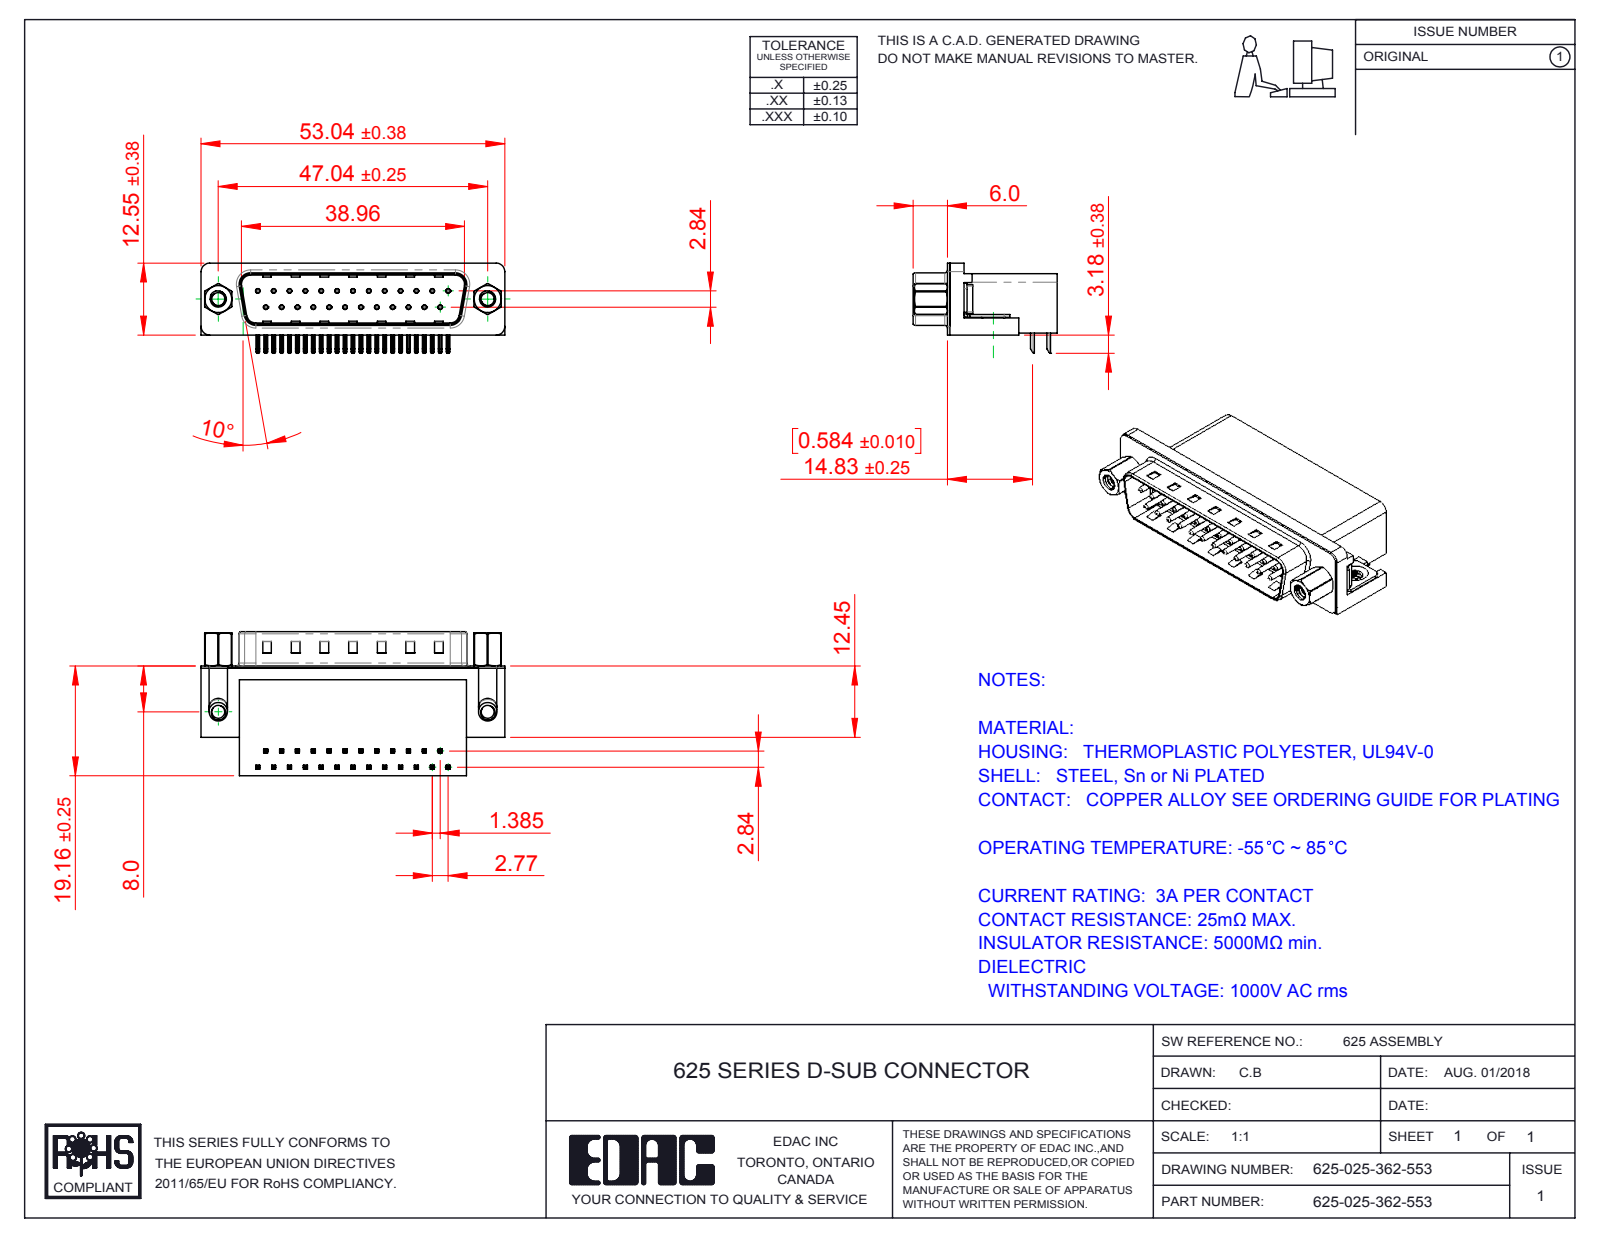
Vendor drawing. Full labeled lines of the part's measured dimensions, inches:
Part name (STEP PRODUCT): 625 Housing_25 Socket; 625 Shell_25 Socket; 625 4-40 Threaded Rivet; 625 Contact Bottom (+4 more)
STEP written by: SolidWorks 2016 (CONFIG_CONTROL_DESIGN)
Units: inches
Bodies: 33 solids, 2423 faces (1429 planar, 745 cylindrical, 249 other)
Overall size (bounding box): 2.088 × 0.991 × 0.619
Volume: 0.573 in³ · Surface area: 14.61 in²
Round holes (diameter × count): ⌀0.014 ×25, ⌀0.031 ×25, ⌀0.089 ×4, ⌀0.09 ×2, ⌀0.157 ×2, ⌀0.189 ×2, ⌀0.197 ×2
Round bosses / shafts (diameter × count): ⌀0.03 ×25, ⌀0.193 ×2, ⌀0.187 ×2, ⌀0.154 ×2, ⌀0.128 ×2, ⌀0.11 ×2
Partial cylindrical surfaces — rounded edges, fillets, slot ends (radius × count): R0.01 ×108, R0.005 ×50, R0.039 ×16, R0.02 ×9, R0.063 ×8, R0.059 ×7, R0.035 ×4, R0.079 ×4
Main face-to-face distances: 0.016, 0.407, 0.739, 0.083, 0.345, 0.412, 0.428, 0.067, 0.754, 0.398
Hole centre spacings: 0.124, 0.109, 0.436, 0.218, 0.327, 0.198, 0.545, 0.294
